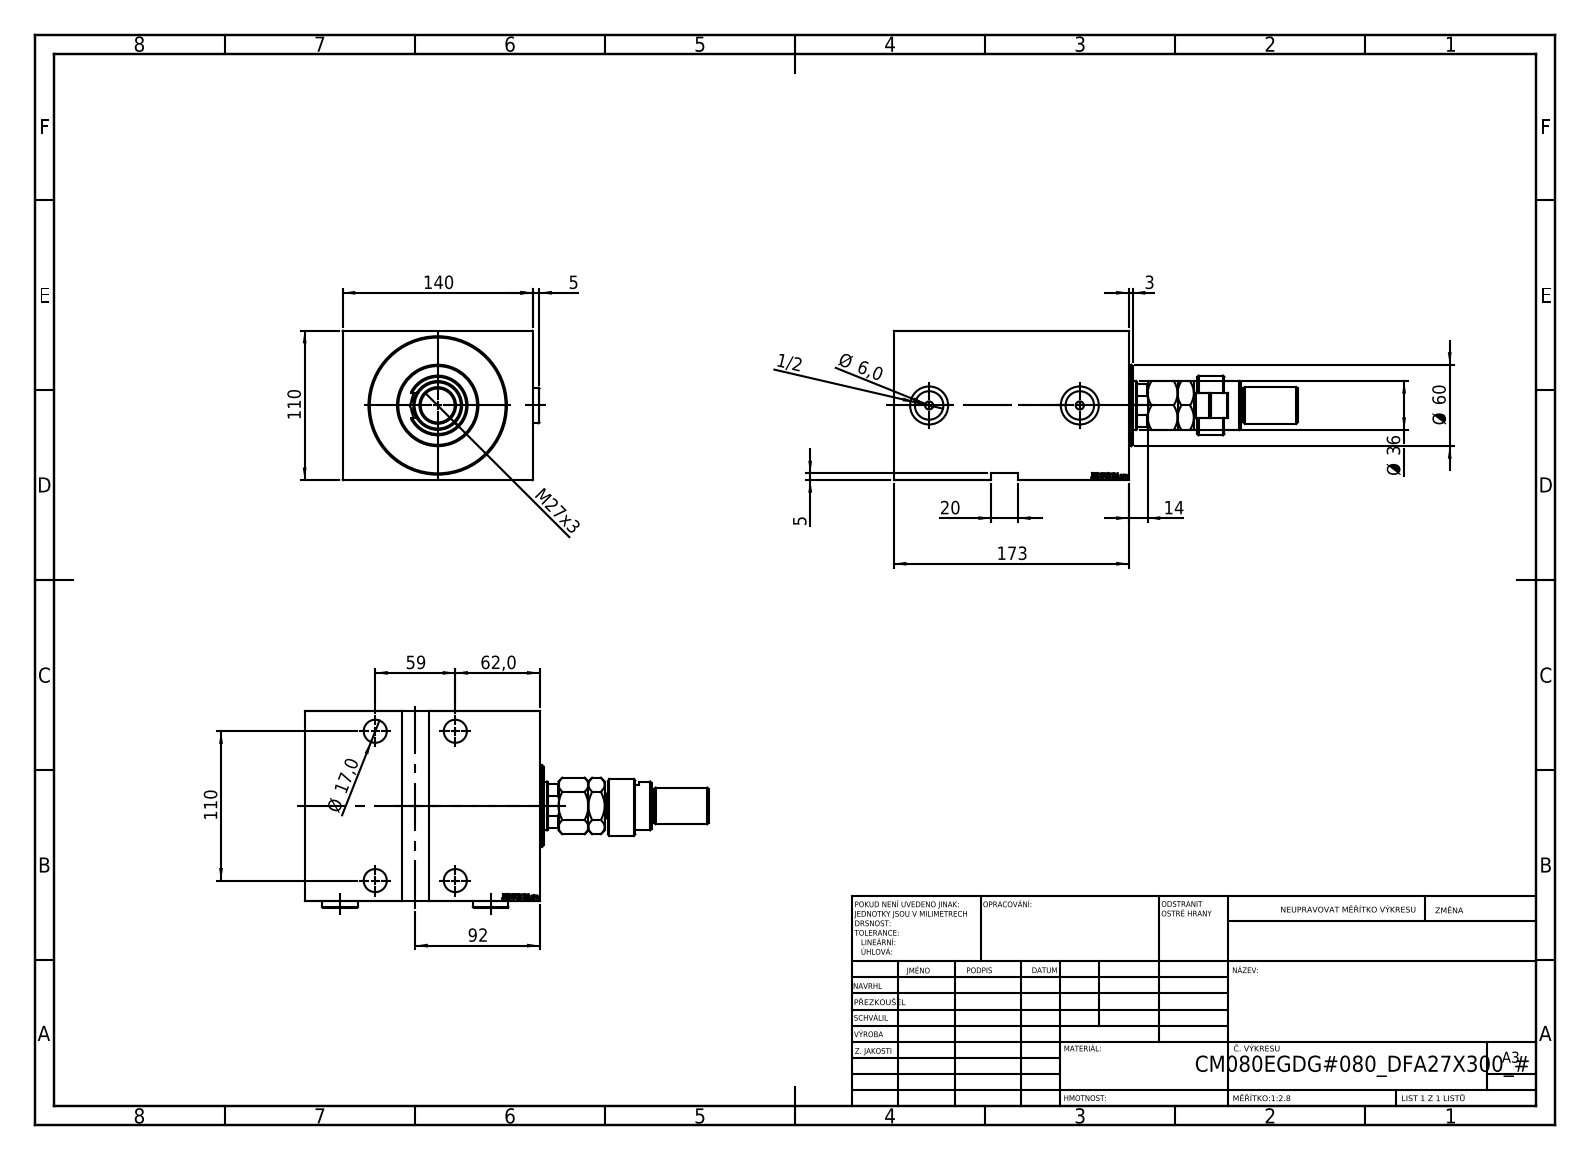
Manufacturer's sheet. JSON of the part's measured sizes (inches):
{"part_name": "MFA; FEMALE_PART_FOR_DFA; V450CM_E_Body; Zatka_OIL_PORT (+2 more)", "step_written_by": "SolidWorks 2019 (CONFIG_CONTROL_DESIGN)", "units": "inches", "bodies": {"solids": 7, "faces": 997, "planar": 474, "cylindrical": 81, "other": 442}, "overall_size": [11.713, 5.705, 4.331], "volume_in3": 140.4, "surface_area_in2": 418.4, "round_holes": [[0.669, 4], [0.984, 4], [0.236, 2], [0.825, 2], [1.102, 2], [1.004, 1], [1.555, 1], [3.15, 1], [3.937, 1]], "round_bosses_or_shafts": [[1.024, 2], [3.228, 1], [2.362, 1], [1.732, 1], [1.417, 1], [1.102, 1], [1.063, 1], [0.984, 1]], "partial_cylinders_radius": [[0.374, 1], [0.591, 1], [0.689, 1]], "face_to_face_distances": [4.331, 5.512, 6.811, 5.984, 0.827, 0.197, 6.614, 5.787, 3.11, 6.157], "hole_center_spacings": [2.323, 4.331, 4.914, 4.37]}
